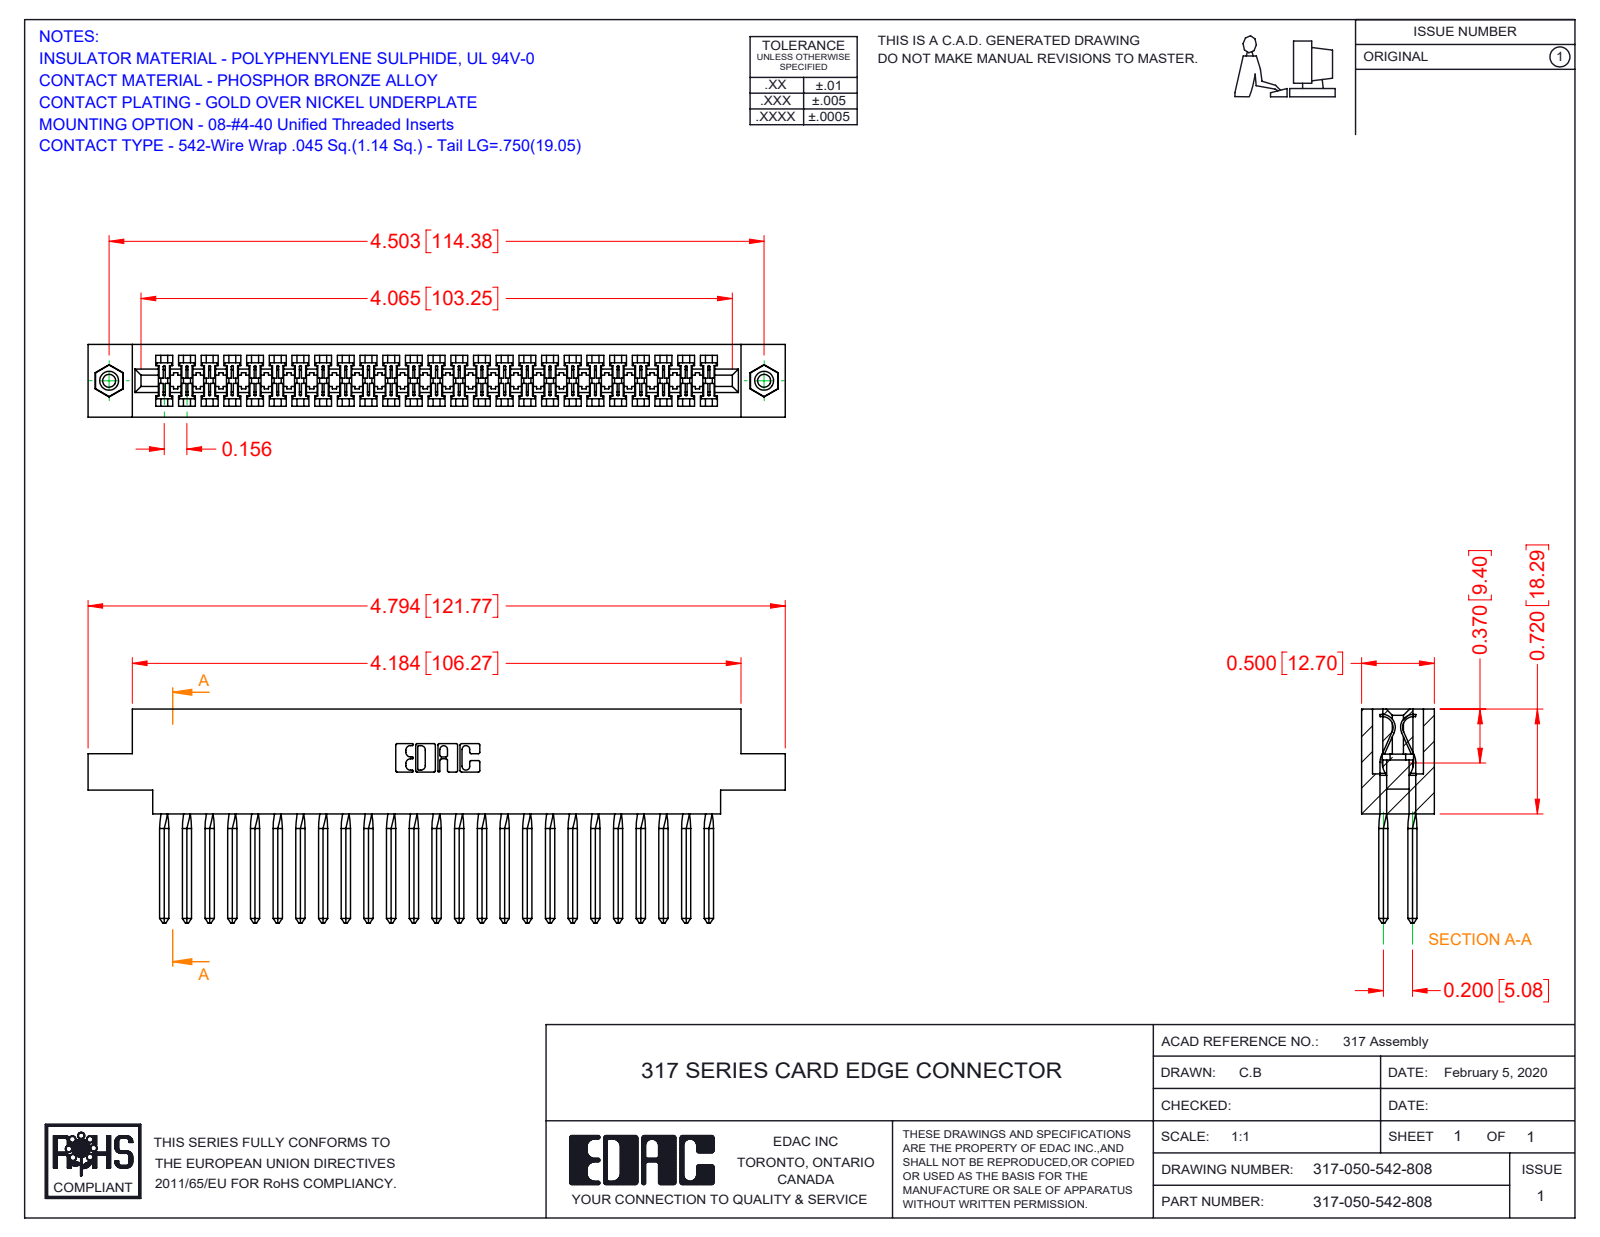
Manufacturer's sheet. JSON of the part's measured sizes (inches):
{"part_name": "317-290-003_542; 345-250-001_345-250-003-102; 317-050-542-808; 317 Part_.156 Dia - TI", "step_written_by": "SolidWorks 2016 (CONFIG_CONTROL_DESIGN)", "units": "inches", "bodies": {"solids": 53, "faces": 3012, "planar": 2390, "cylindrical": 406, "other": 216}, "overall_size": [4.794, 1.47, 0.5], "volume_in3": 1.184, "surface_area_in2": 40.99, "round_holes": [[0.089, 2], [0.125, 2], [0.156, 2]], "round_bosses_or_shafts": [[0.155, 2]], "partial_cylinders_radius": [[0.006, 100], [0.01, 22], [0.007, 6], [0.031, 6], [0.026, 3], [0.074, 2], [0.089, 2], [0.1, 2]], "face_to_face_distances": [0.5, 0.075, 0.425, 0.35, 0.2, 0.11, 0.116, 0.136, 0.046, 0.72], "hole_center_spacings": [4.503]}
